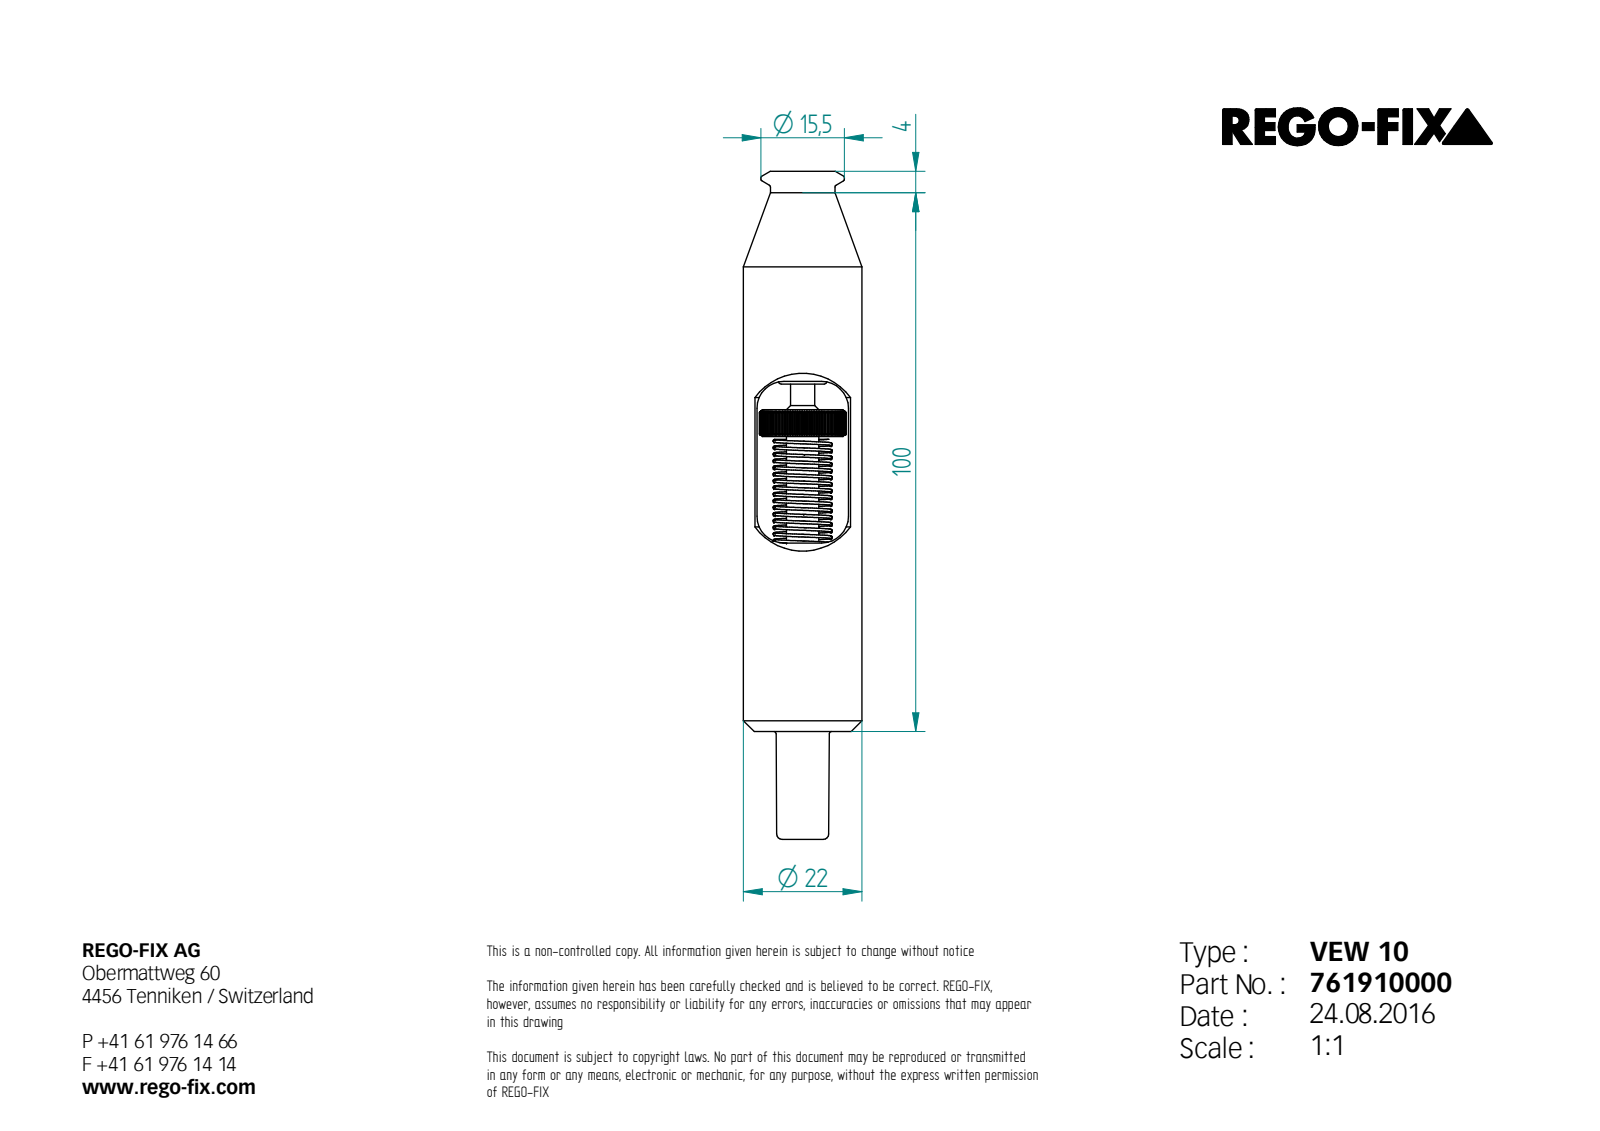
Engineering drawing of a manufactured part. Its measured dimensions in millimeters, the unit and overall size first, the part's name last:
Units: millimetres
Overall size (bounding box): 124 × 22 × 22
Round holes (diameter × count): ⌀4 ×1, ⌀4.92 ×1, ⌀6.1 ×1, ⌀6.19 ×1, ⌀7.2 ×1, ⌀10 ×1
Round bosses / shafts (diameter × count): ⌀22 ×1, ⌀15.5 ×1, ⌀12 ×1, ⌀9.7 ×1, ⌀9 ×1, ⌀6 ×1, ⌀4.5 ×1
Partial cylindrical surfaces — rounded edges, fillets, slot ends (radius × count): R5 ×4, R8 ×1
Main face-to-face distances: 17, 7.76, 54.75, 59.75, 5, 35, 19.75, 24.75, 104, 69
Volume: 27 554 mm³ · Surface area: 14 657 mm²
Bodies: 5 solids, 533 faces (338 planar, 170 cylindrical, 25 other)
Part name (STEP PRODUCT): 0003754; 0007697; 0007711; 0003773-oa0 (+1 more)
STEP written by: Unknown (AUTOMOTIVE_DESIGN)
